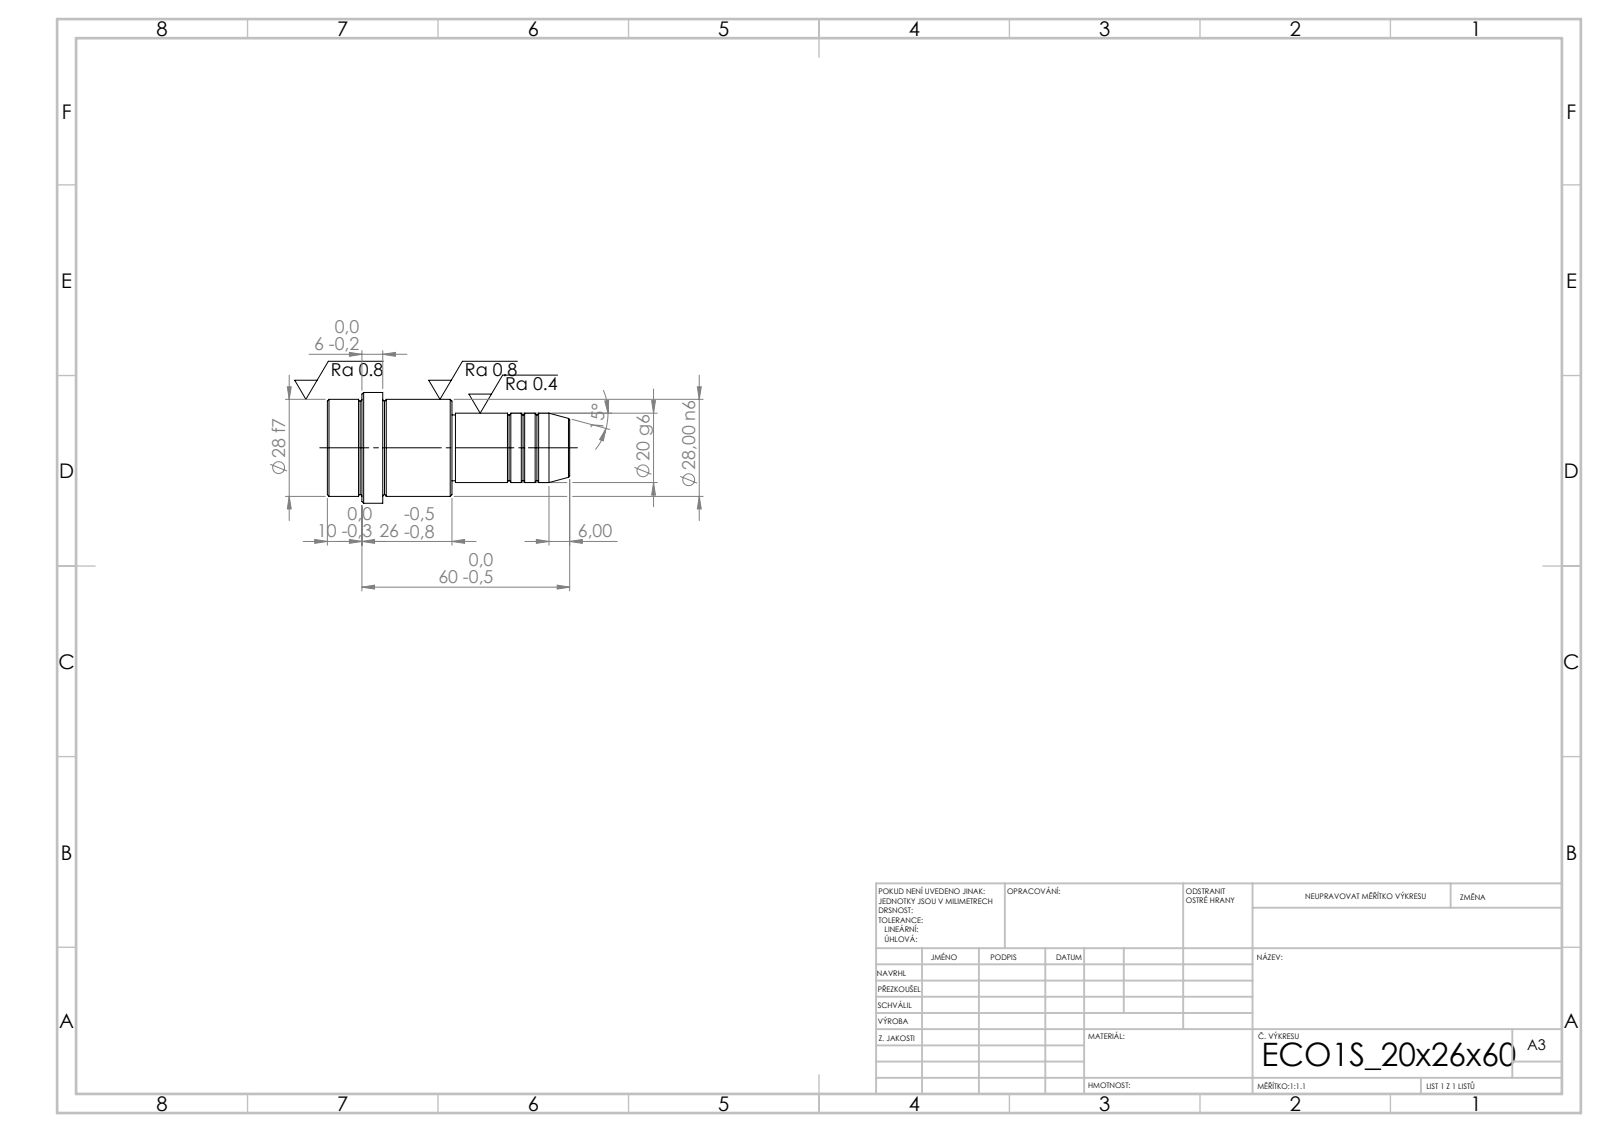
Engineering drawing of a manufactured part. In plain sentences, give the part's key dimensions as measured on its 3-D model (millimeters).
Its 3-D file was written by "SolidWorks 2019 (CONFIG_CONTROL_DESIGN)". It is 1 solid with 52 faces: 6 planar, 16 cylindrical and 30 other. Overall it measures 70 by 32 by 32 millimeters. Its volume is 33 486 cubic millimeters and its surface area 7 038 square millimeters. Round bosses or shafts: 1 of diameter 32, 1 of diameter 28, 1 of diameter 20, 1 of diameter 19. The main face-to-face distances are 36, 34, 70, 54, 20, 16, 60, 26, 6, 10.
